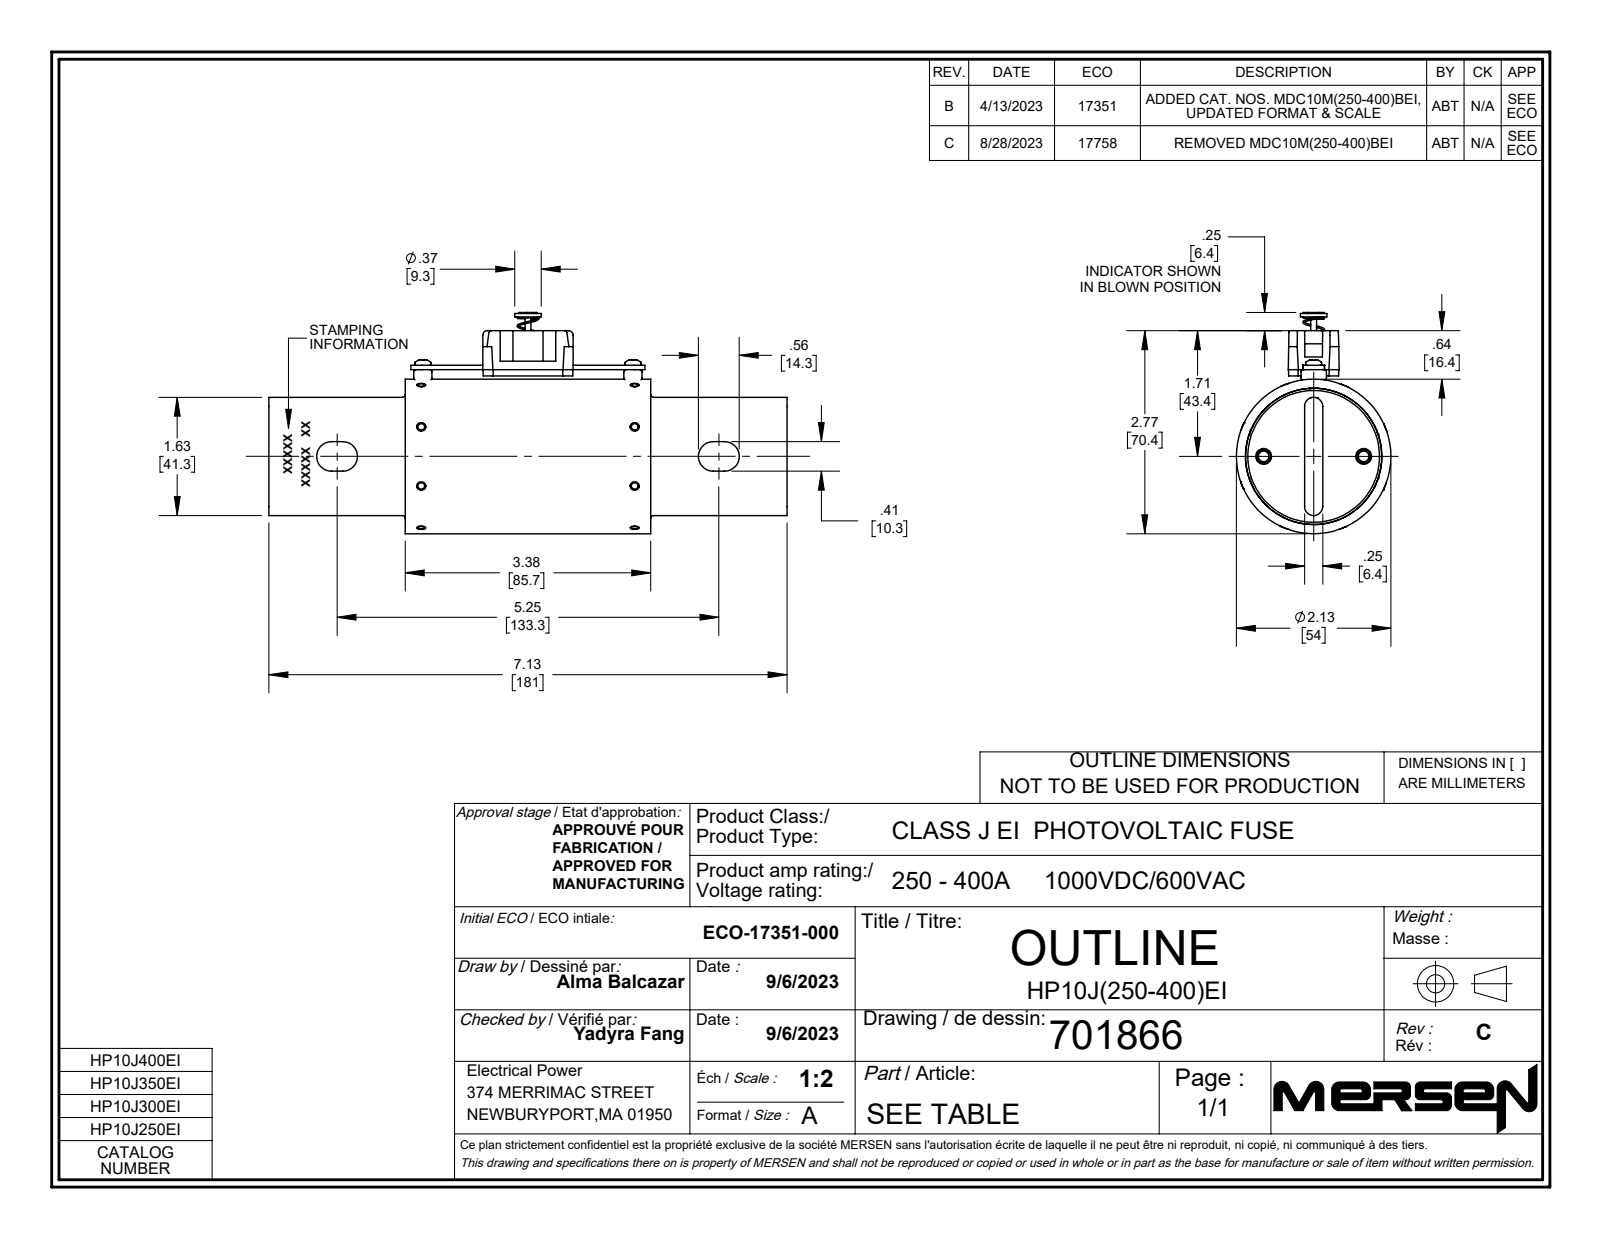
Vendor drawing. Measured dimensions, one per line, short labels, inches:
name: 104265; 102173^340020; 9399_9399; 102062_102062 (+8 more)
written by: SolidWorks 2021 (CONFIG_CONTROL_DESIGN)
unit: in
bodies: 40 solids, 2809 faces (782 planar, 1208 cylindrical, 819 other)
size: 7.125 × 3.041 × 2.125
volume: 6.761 in³; area: 93.9 in²
holes: 18× ⌀0.125, 3× ⌀0.17, 2× ⌀0.101, 2× ⌀0.146, 2× ⌀0.187, 1× ⌀1.875
bosses: 2× ⌀0.219, 2× ⌀0.192, 2× ⌀0.112, 2× ⌀0.08, 1× ⌀2.125, 1× ⌀1.872, 1× ⌀0.365, 1× ⌀0.081
rounds: 52× R4, 22× R0.03, 14× R0.005, 10× R0.02, 10× R0.06, 4× R0.04, 4× R0.07, 4× R0.203
face distances: 0.25, 0.438, 2.937, 3.375, 2.499, 0.38, 0.06, 0.287, 1.875, 2.313
hole spacings: 2.935, 0.19, 0.687, 1.254, 1.444, 1.635, 0.38, 1.375
